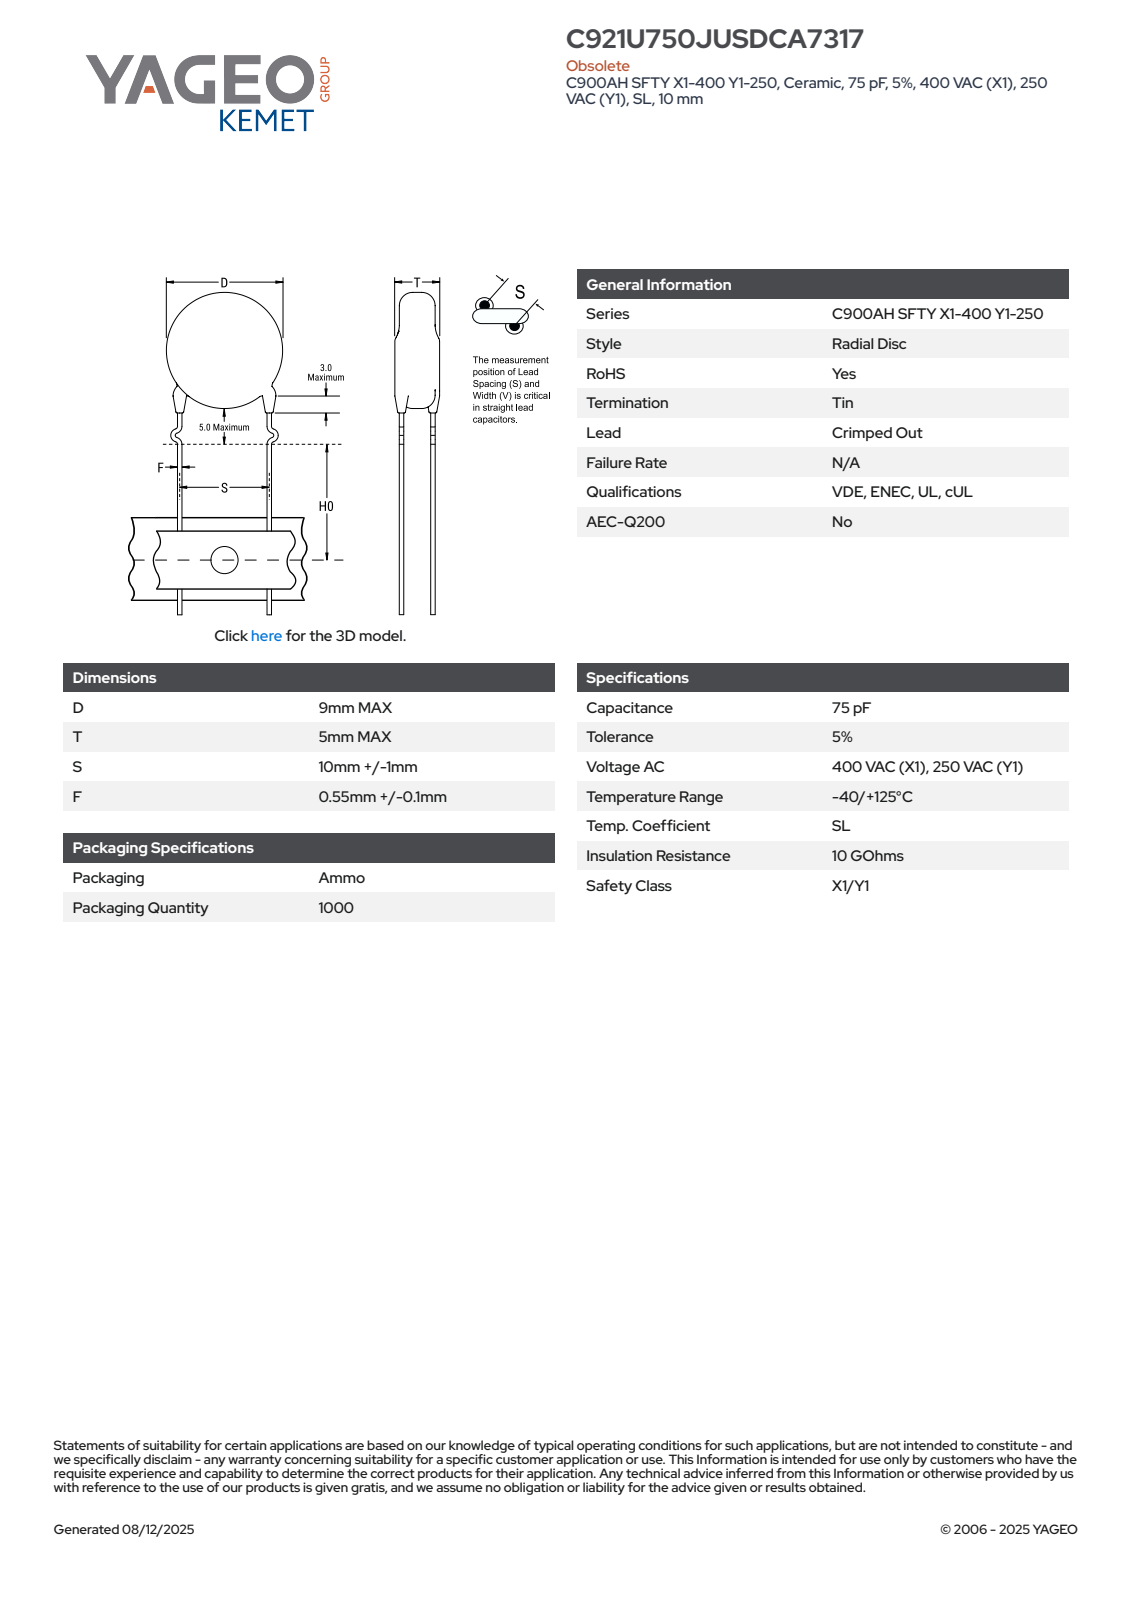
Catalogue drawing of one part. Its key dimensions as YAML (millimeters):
part_name: "CCD_KCOC900_D9T5S10LL20F0.55"
step_written_by: "SolidWorks 2014 (AUTOMOTIVE_DESIGN)"
units: millimeters
bodies: {solids: 4, faces: 93, planar: 63, cylindrical: 10, other: 20}
overall_size: [34, 14.51, 5.85]
volume: 332
surface_area: 386
round_bosses_or_shafts:
  - {diameter: 1.2, count: 2}
  - {diameter: 9, count: 1}
partial_cylinders:
  - {radius: 0.6, count: 2}
face_to_face_distances: [5, 0.94, 4.98, 4.04, 0.76, 3.82, 0.58, 4.07, 2.77, 2.88]
